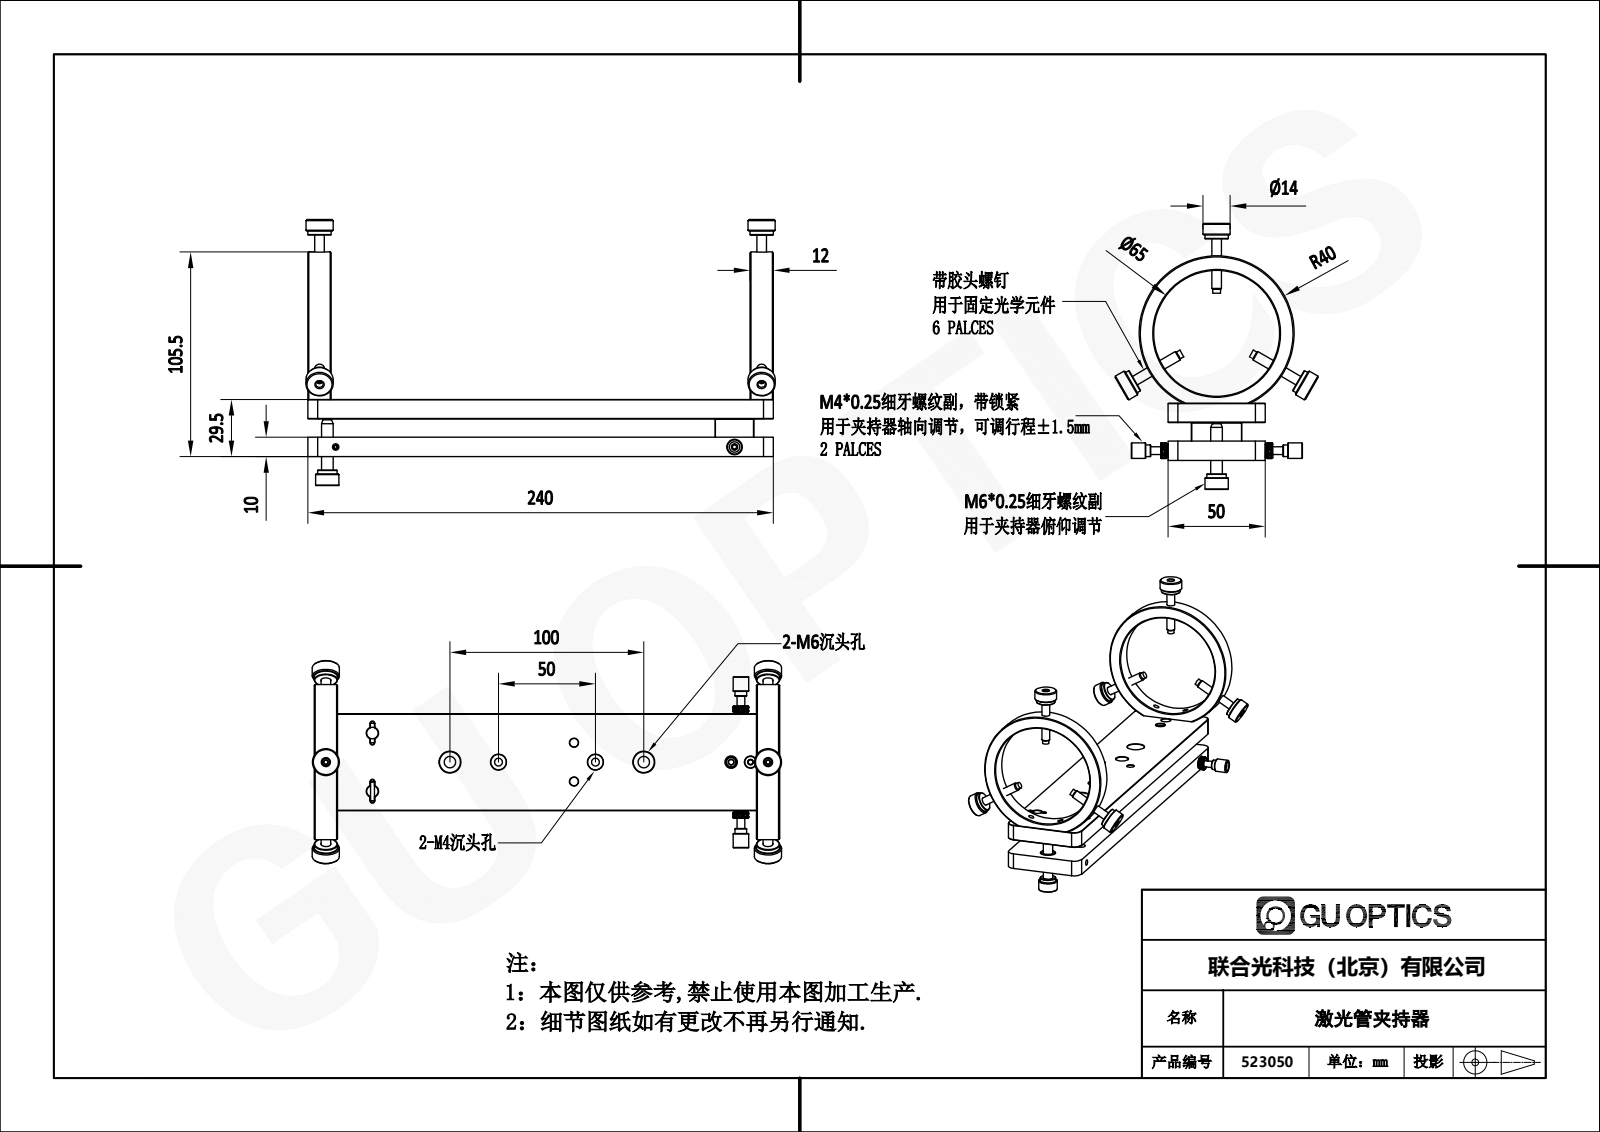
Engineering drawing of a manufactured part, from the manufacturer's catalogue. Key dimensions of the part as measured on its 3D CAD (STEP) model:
Part name (STEP PRODUCT): 523050
STEP written by: SolidWorks 2020 (CONFIG_CONTROL_DESIGN)
Units: millimetres
Bodies: 36 solids, 1499 faces (620 planar, 382 cylindrical, 497 other)
Overall size (bounding box): 242 × 137.14 × 104.72
Volume: 278 834 mm³ · Surface area: 95 449 mm²
Round holes (diameter × count): ⌀1.5 ×10, ⌀8 ×8, ⌀6 ×7, ⌀3.8 ×6, ⌀4.2 ×6, ⌀4.5 ×6, ⌀5.2 ×6, ⌀3.3 ×4, ⌀4 ×4, ⌀2.5 ×3, ⌀1 ×2, ⌀3 ×2
Round bosses / shafts (diameter × count): ⌀12 ×7, ⌀5 ×7, ⌀4 ×7, ⌀14 ×6, ⌀80 ×1, ⌀10 ×1, ⌀9.5 ×1, ⌀8.6 ×1
Partial cylindrical surfaces — rounded edges, fillets, slot ends (radius × count): R1.05 ×6, R5 ×6, R6 ×2, R4.29 ×1
Main face-to-face distances: 10, 19.5, 9.5, 29.5, 50, 12, 228, 240, 216, 2
Hole centre spacings: 54.68, 25, 64.78, 10, 228, 89.56, 114.44, 139.36
